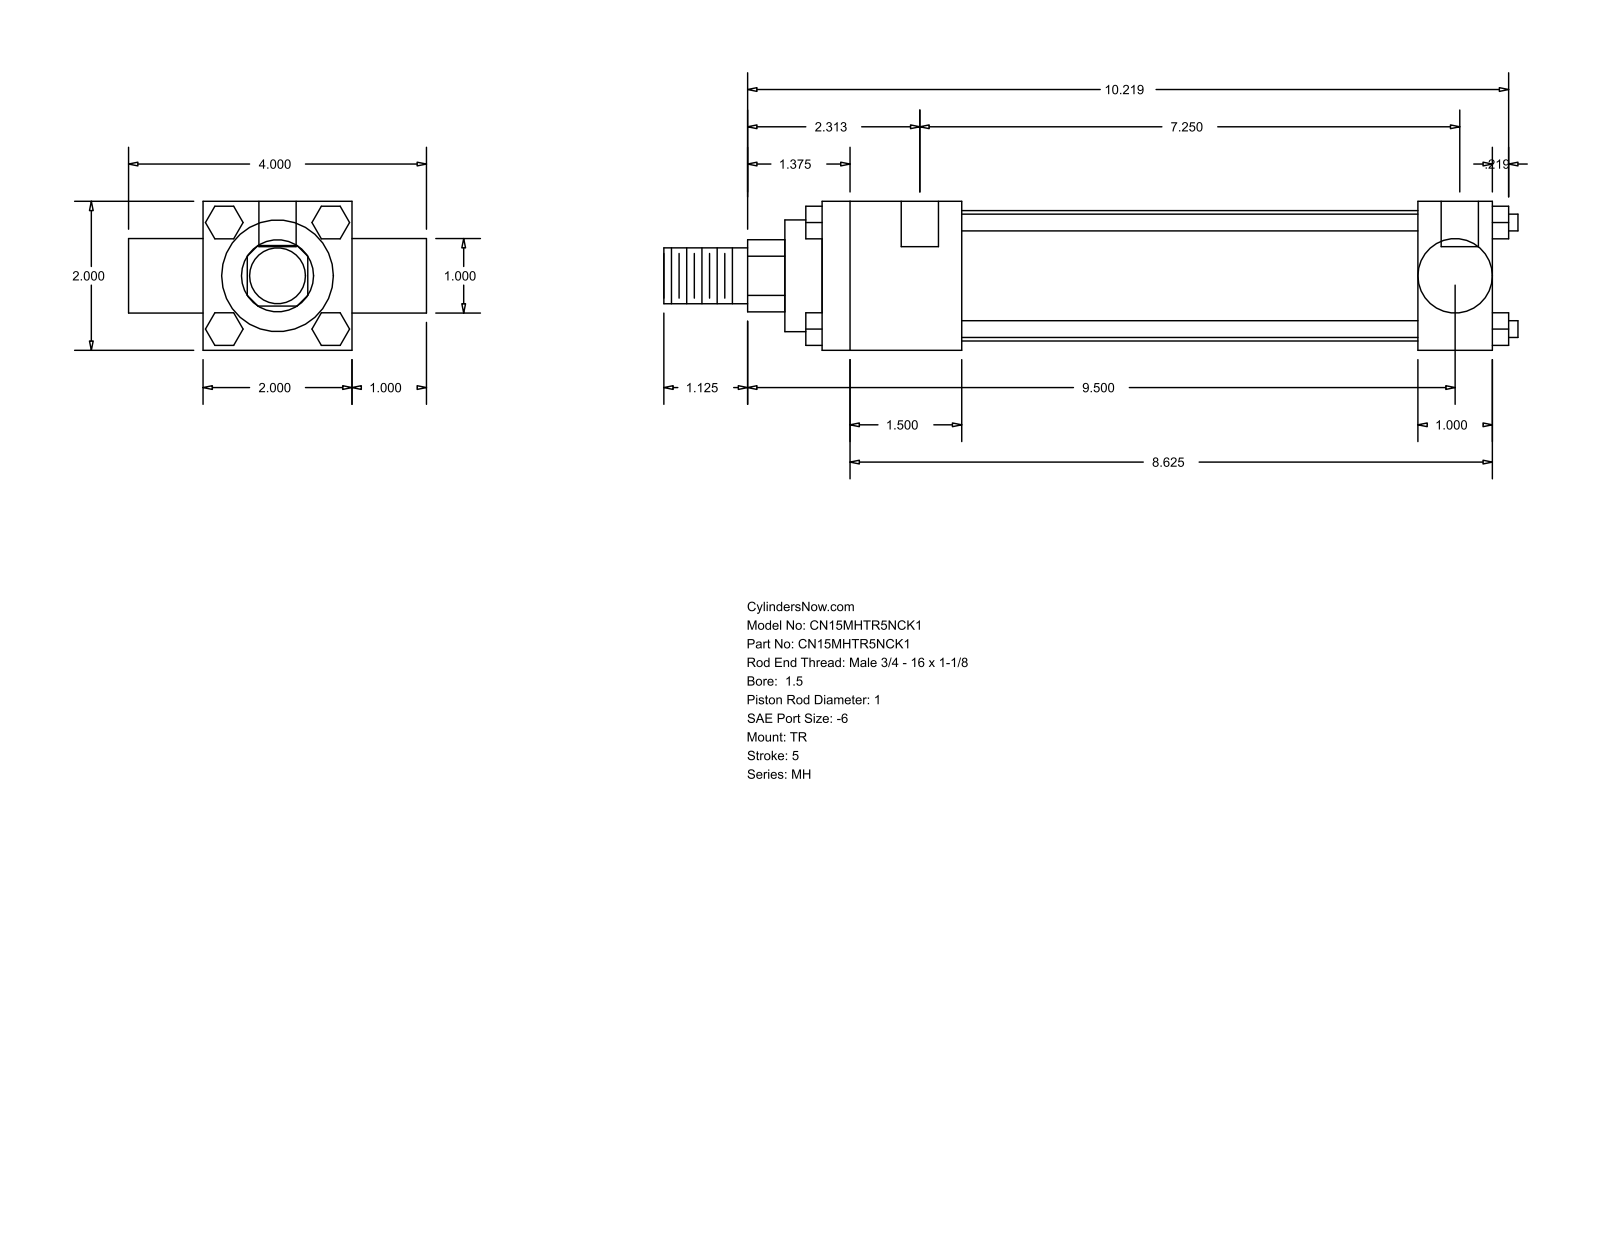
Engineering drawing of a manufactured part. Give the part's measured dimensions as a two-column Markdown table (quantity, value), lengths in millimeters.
| quantity | value |
| --- | --- |
| part name | MH_TR__0150_1 |
| STEP written by | GSSL Pune (CONFIG_CONTROL_DESIGN) |
| units | millimeters |
| bodies | 0 solids, 120 faces (92 planar, 28 cylindrical, 0 other) |
| overall size | 291.31 × 101.6 × 50.8 |
| round holes (diameter × count) | 5.56 × 3, 12.7 × 2 |
| round bosses / shafts (diameter × count) | 5.71 × 4, 44.45 × 1, 38.1 × 1, 25.4 × 1, 25.35 × 1, 19.05 × 1 |
| partial cylindrical surfaces (radius × count) | 12.29 × 1 |
| main face-to-face distances | 50.8, 25.4, 228.6, 76.2, 47.63, 180.97, 203.2, 155.57, 101.6, 12.7 |
| hole center spacings | 3.18, 184.15, 187.33 |
